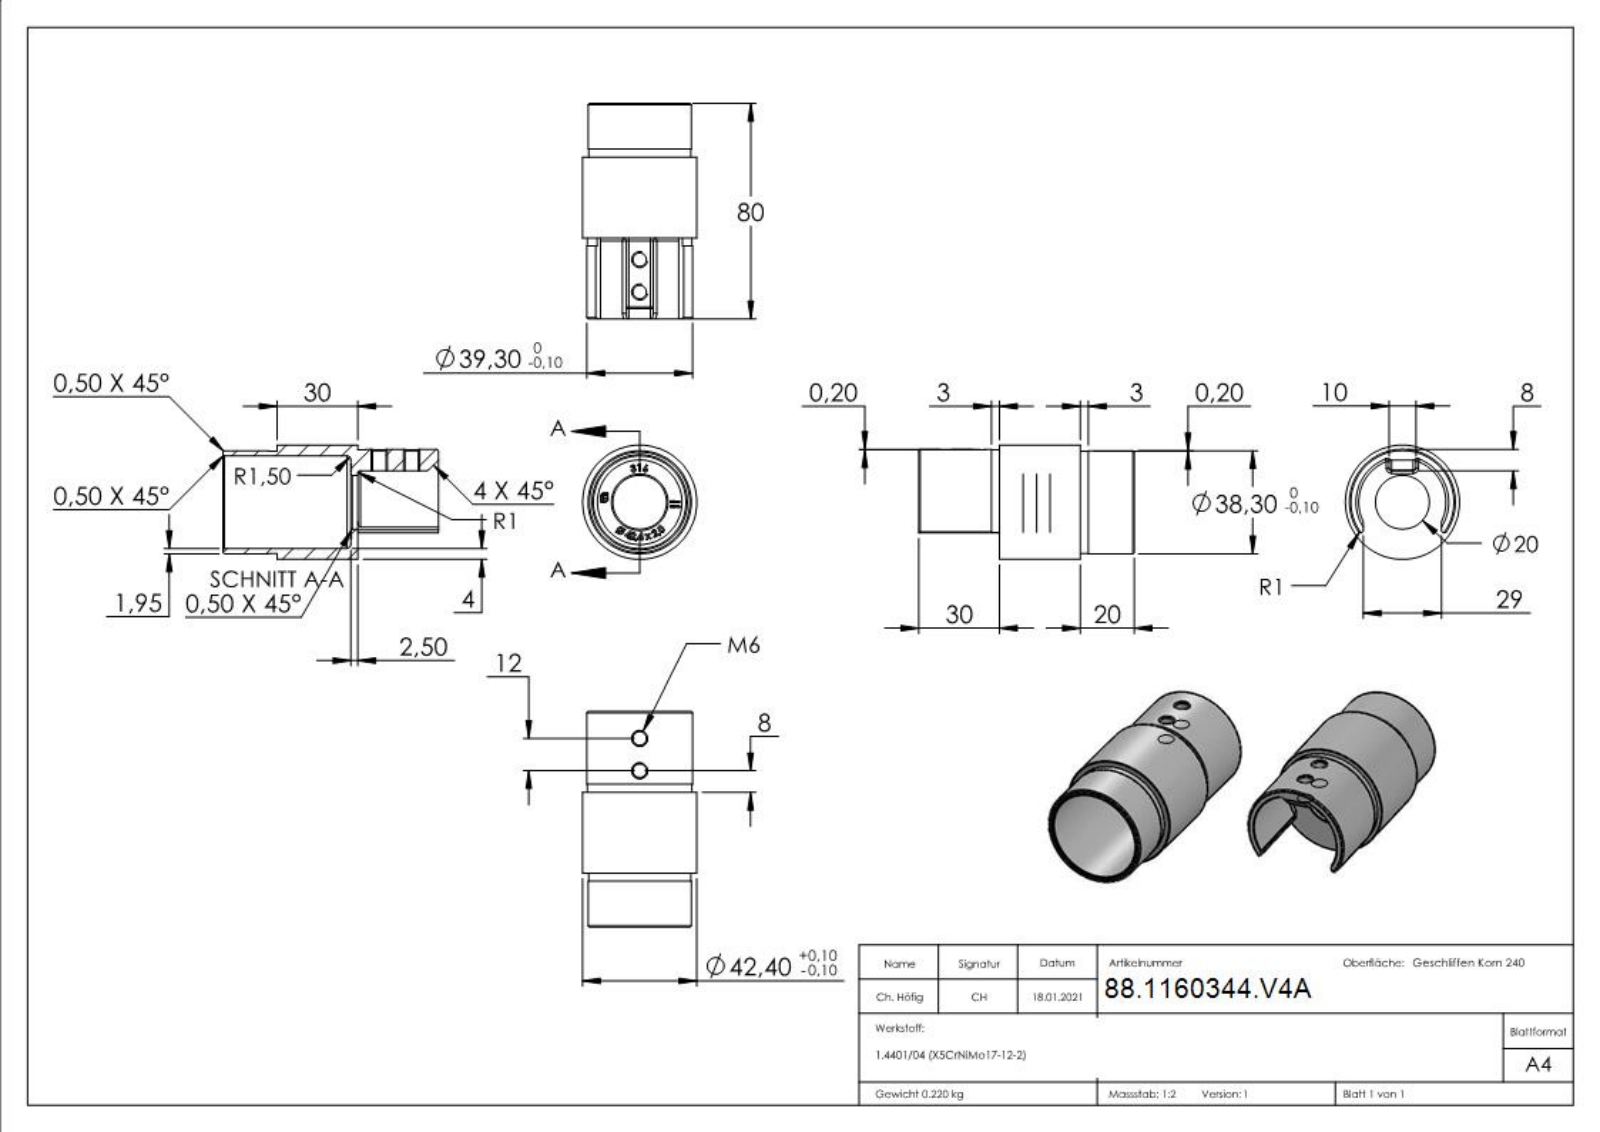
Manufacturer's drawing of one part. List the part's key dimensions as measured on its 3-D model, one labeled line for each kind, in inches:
Part name (STEP PRODUCT): 60344-V4A
STEP written by: SolidWorks 2018 (CONFIG_CONTROL_DESIGN)
Units: inches
Bodies: 1 solid, 497 faces (281 planar, 35 cylindrical, 181 other)
Overall size (bounding box): 3.15 × 1.669 × 1.669
Volume: 1.679 in³ · Surface area: 29.55 in²
Round holes (diameter × count): ⌀0.197 ×2, ⌀0.787 ×1, ⌀1.354 ×1
Round bosses / shafts (diameter × count): ⌀1.669 ×1, ⌀1.508 ×1, ⌀1.492 ×1
Partial cylindrical surfaces — rounded edges, fillets, slot ends (radius × count): R0.039 ×12, R0.766 ×1, R0.774 ×1
Main face-to-face distances: 1.181, 0.098, 1.083, 1.28, 2.362, 3.15, 1.969, 1.87, 0.787, 0.374
Hole centre spacings: 0.472
